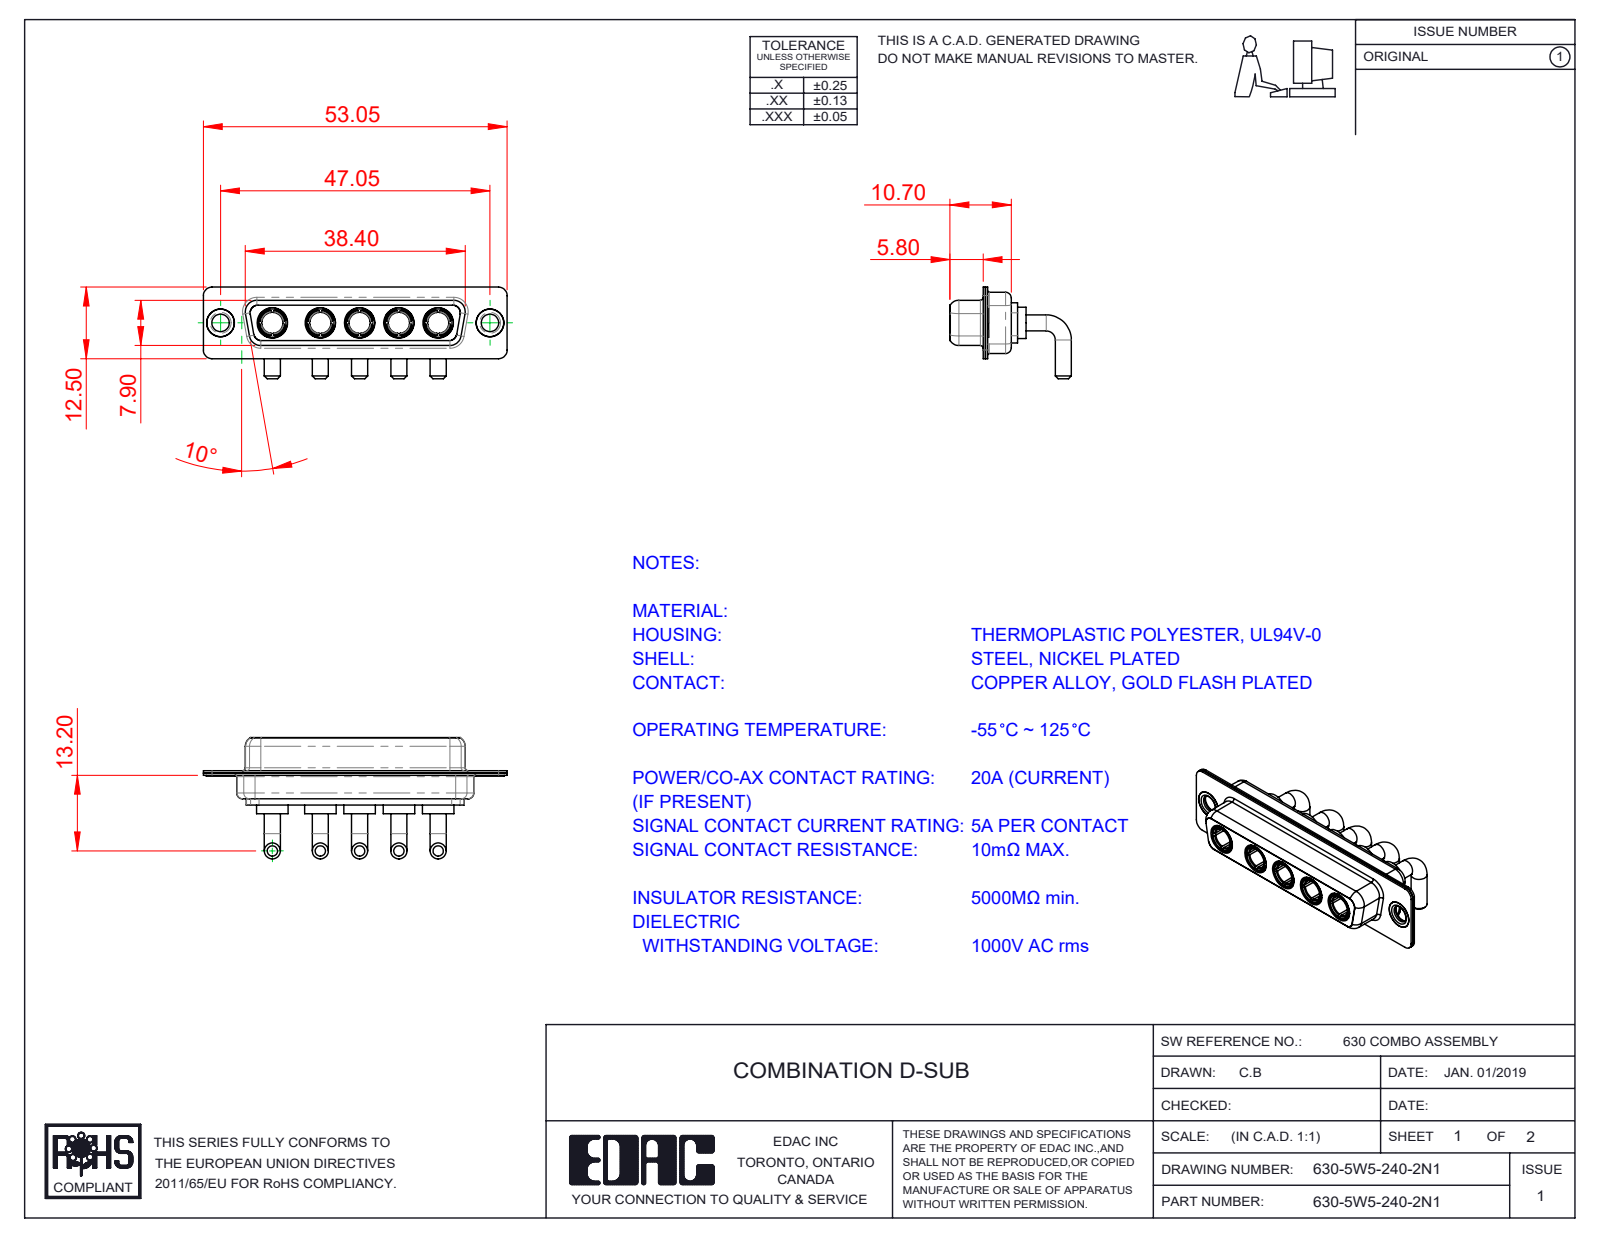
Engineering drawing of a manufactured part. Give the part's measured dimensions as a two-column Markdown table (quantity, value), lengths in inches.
| quantity | value |
| --- | --- |
| part name | 630-5W5-240-2N1; Power Socket_20A RA; 630Combo Shell Front_25 Contacts; 630Combo Thru Hole Rivet (+2 more) |
| STEP written by | SolidWorks 2020 (CONFIG_CONTROL_DESIGN) |
| units | inches |
| bodies | 15 solids, 643 faces (212 planar, 246 cylindrical, 185 other) |
| overall size | 2.089 × 0.835 × 0.63 |
| volume | 0.241 in³ |
| surface area | 13.24 in² |
| round holes (diameter × count) | 0.191 × 7, 0.146 × 5, 0.209 × 5, 0.12 × 2, 0.157 × 2, 0.159 × 2 |
| round bosses / shafts (diameter × count) | 0.11 × 10, 0.217 × 5, 0.205 × 5, 0.195 × 5, 0.187 × 5, 0.148 × 5, 0.197 × 2, 0.195 × 2 |
| partial cylindrical surfaces (radius × count) | 0.059 × 16, 0.079 × 12, 0.053 × 8, 0.063 × 8, 0.083 × 5, 0.01 × 4, 0.02 × 4, 0.024 × 4 |
| main face-to-face distances | 0.016, 0.018, 0.055, 0.333, 0.35, 0.071, 0.278, 0.244, 0.295, 0.073 |
| hole center spacings | 0.27, 0.356, 1.496, 0.27, 0.33, 0.54, 0.541, 0.6 |
